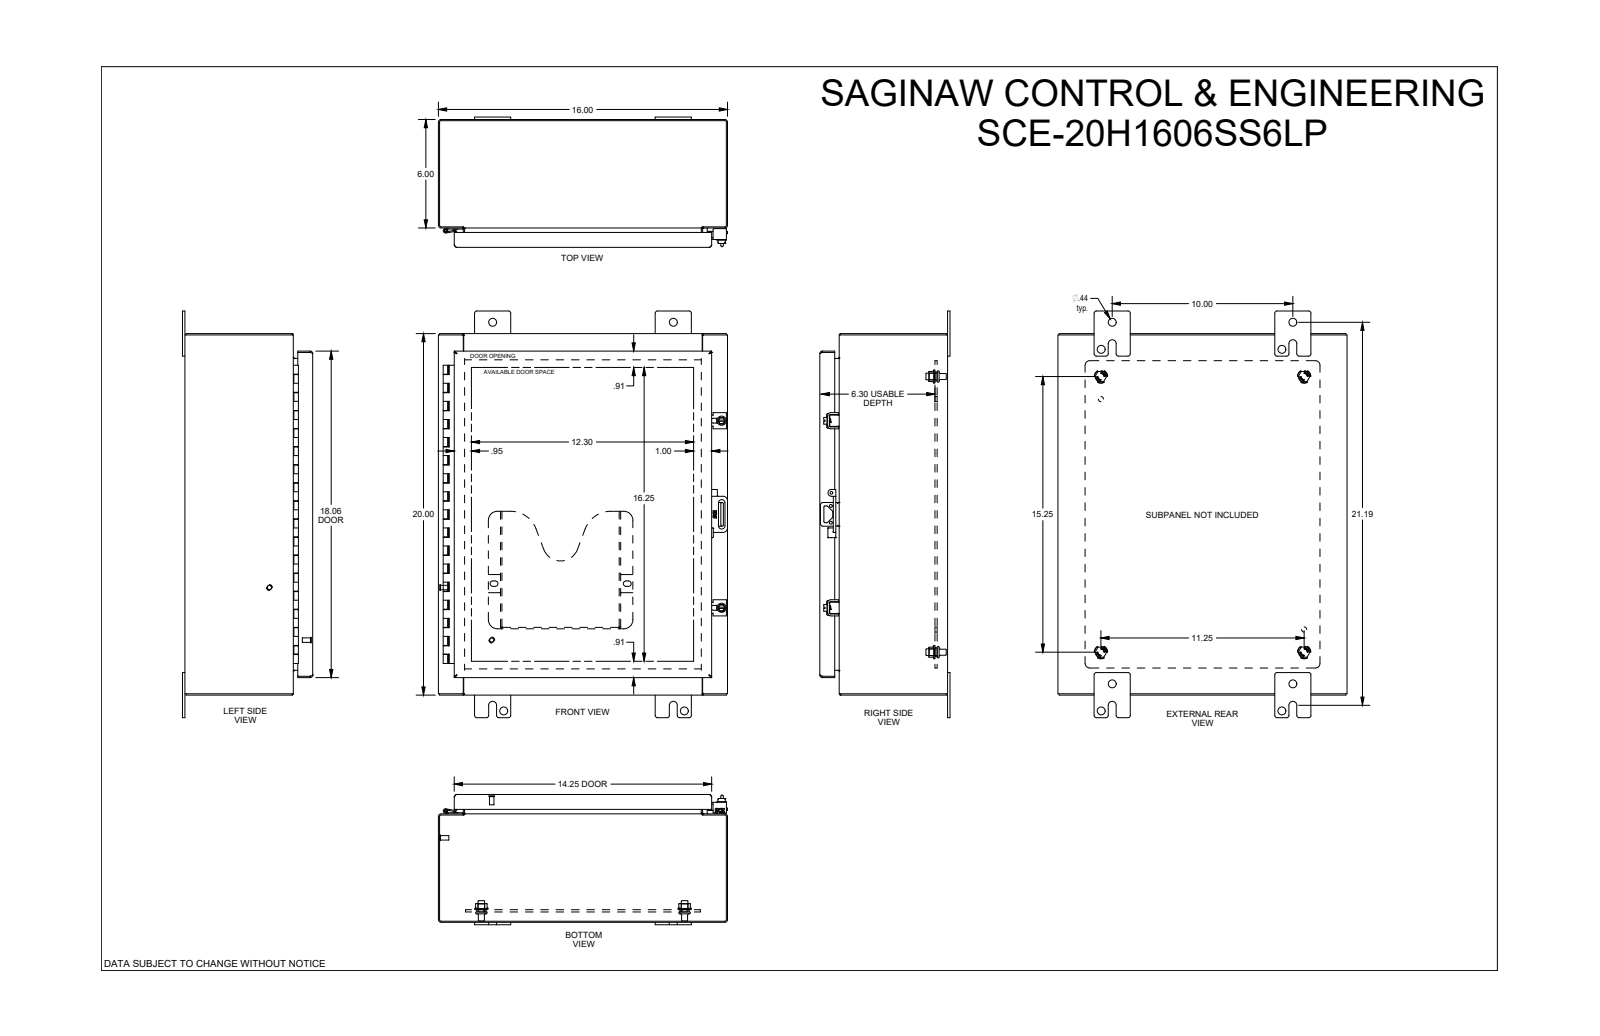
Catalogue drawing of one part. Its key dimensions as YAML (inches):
part_name: "SCE-20H1606LP"
step_written_by: "SolidWorks 2021 (AUTOMOTIVE_DESIGN)"
units: inches
bodies: {solids: 38, faces: 1990, planar: 777, cylindrical: 830, other: 383}
overall_size: [22.5, 16, 7.343]
volume: 135.6
surface_area: 3202
round_holes:
  - {diameter: 0.172, count: 4}
  - {diameter: 0.205, count: 4}
  - {diameter: 0.218, count: 4}
  - {diameter: 0.244, count: 4}
  - {diameter: 0.312, count: 4}
  - {diameter: 0.375, count: 4}
  - {diameter: 0.437, count: 4}
  - {diameter: 0.5, count: 4}
  - {diameter: 0.04, count: 2}
  - {diameter: 0.16, count: 2}
  - {diameter: 0.188, count: 2}
  - {diameter: 0.203, count: 2}
round_bosses_or_shafts:
  - {diameter: 0.248, count: 7}
  - {diameter: 0.25, count: 6}
  - {diameter: 0.59, count: 4}
  - {diameter: 0.376, count: 4}
  - {diameter: 0.375, count: 4}
  - {diameter: 0.33, count: 4}
  - {diameter: 0.31, count: 4}
  - {diameter: 0.24, count: 4}
partial_cylinders:
  - {radius: 0.025, count: 68}
  - {radius: 0.01, count: 62}
  - {radius: 0.03, count: 32}
  - {radius: 0.06, count: 28}
  - {radius: 0.015, count: 24}
  - {radius: 0.185, count: 21}
  - {radius: 0.04, count: 18}
  - {radius: 0.22, count: 16}
face_to_face_distances: [0.075, 0.06, 6.993, 7.068, 7.008, 6.933, 15.925, 6.493, 0.575, 0.5]
hole_center_spacings: [1.741, 2.25, 10.749, 12.25, 16.887, 19.942, 10, 0.493]
